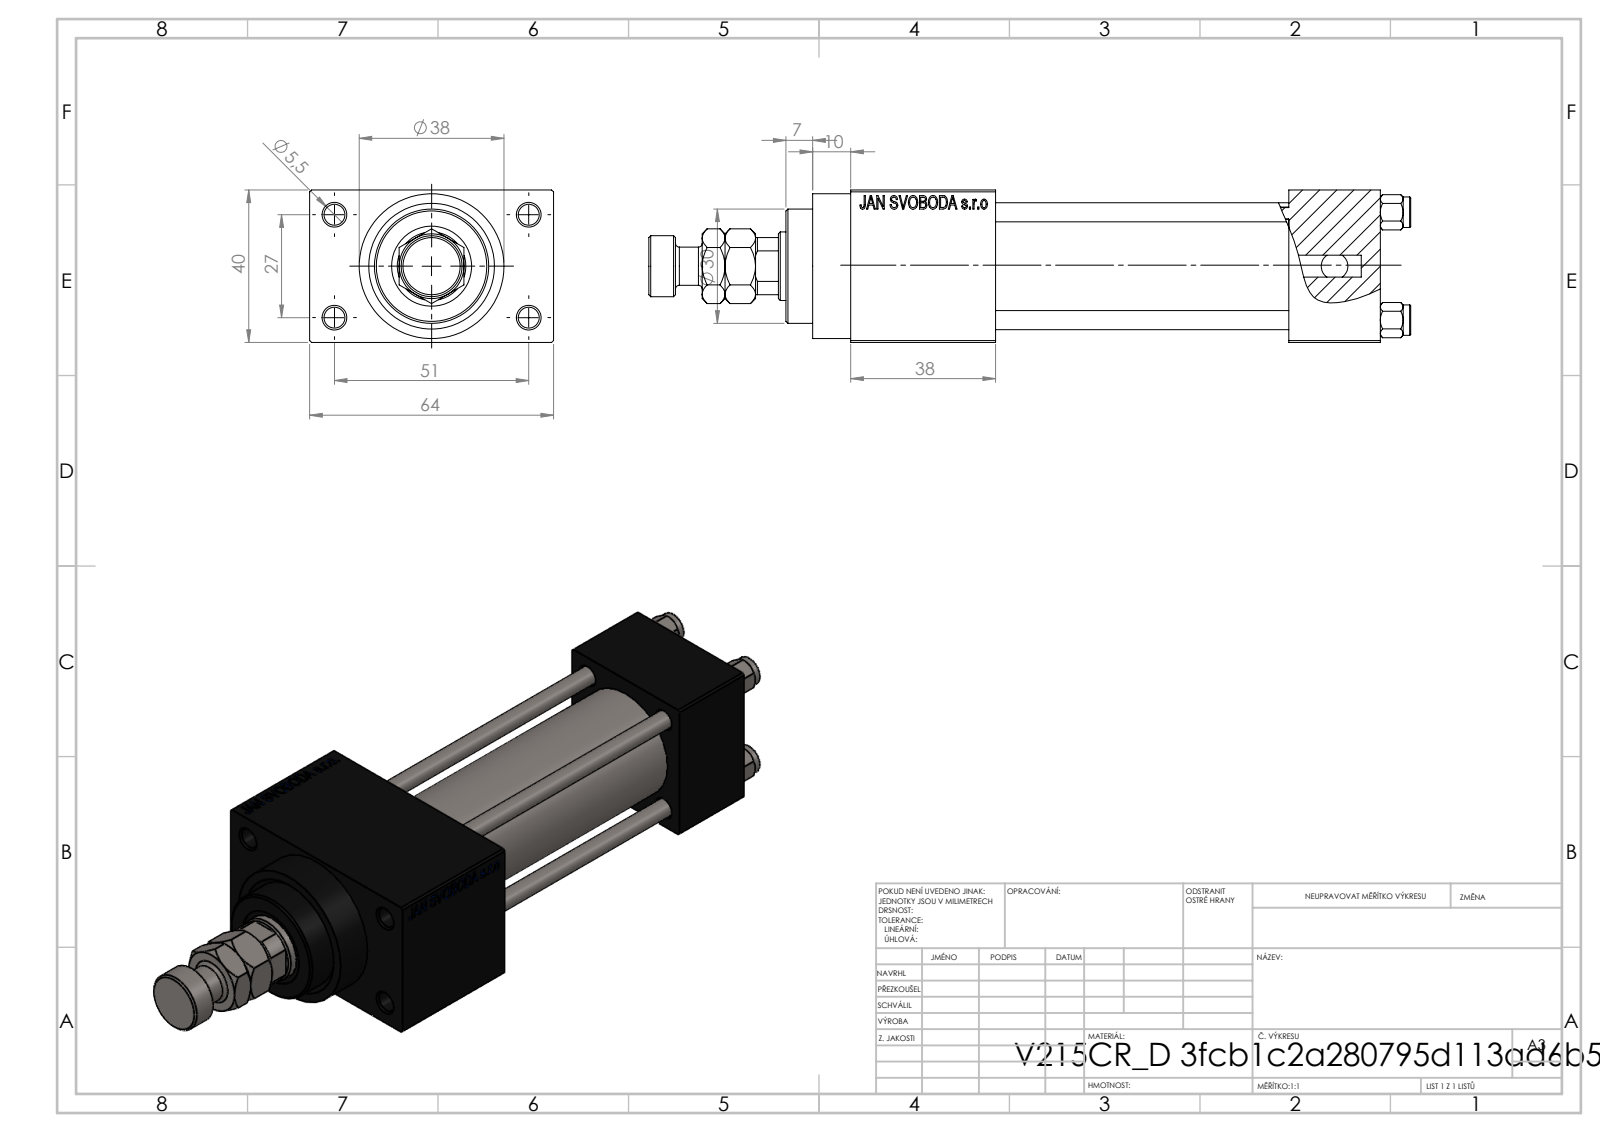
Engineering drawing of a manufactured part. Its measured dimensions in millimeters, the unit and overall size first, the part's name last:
Units: millimetres
Overall size (bounding box): 200 × 64 × 40
Round holes (diameter × count): ⌀5 ×4, ⌀5.5 ×4, ⌀20 ×3, ⌀7 ×2, ⌀13.16 ×2, ⌀8.5 ×1, ⌀18 ×1, ⌀21 ×1, ⌀25 ×1, ⌀30 ×1
Round bosses / shafts (diameter × count): ⌀8 ×4, ⌀38 ×1, ⌀31 ×1, ⌀16 ×1, ⌀10 ×1
Partial cylindrical surfaces — rounded edges, fillets, slot ends (radius × count): R8.5 ×1
Main face-to-face distances: 40, 77, 12, 24, 101, 52, 38, 139, 115, 64
Hole centre spacings: 11.37, 20.01, 28.3, 28.85, 29.89, 39.66, 48.34, 27
Volume: 202 455 mm³ · Surface area: 75 554 mm²
Bodies: 12 solids, 1153 faces (511 planar, 90 cylindrical, 552 other)
Part name (STEP PRODUCT): V215CR_VCP_D; V215CR_D_Body; V215CR_D_TYCINKA; NUT_M5_D (+2 more)
STEP written by: SolidWorks 2019 (CONFIG_CONTROL_DESIGN)
